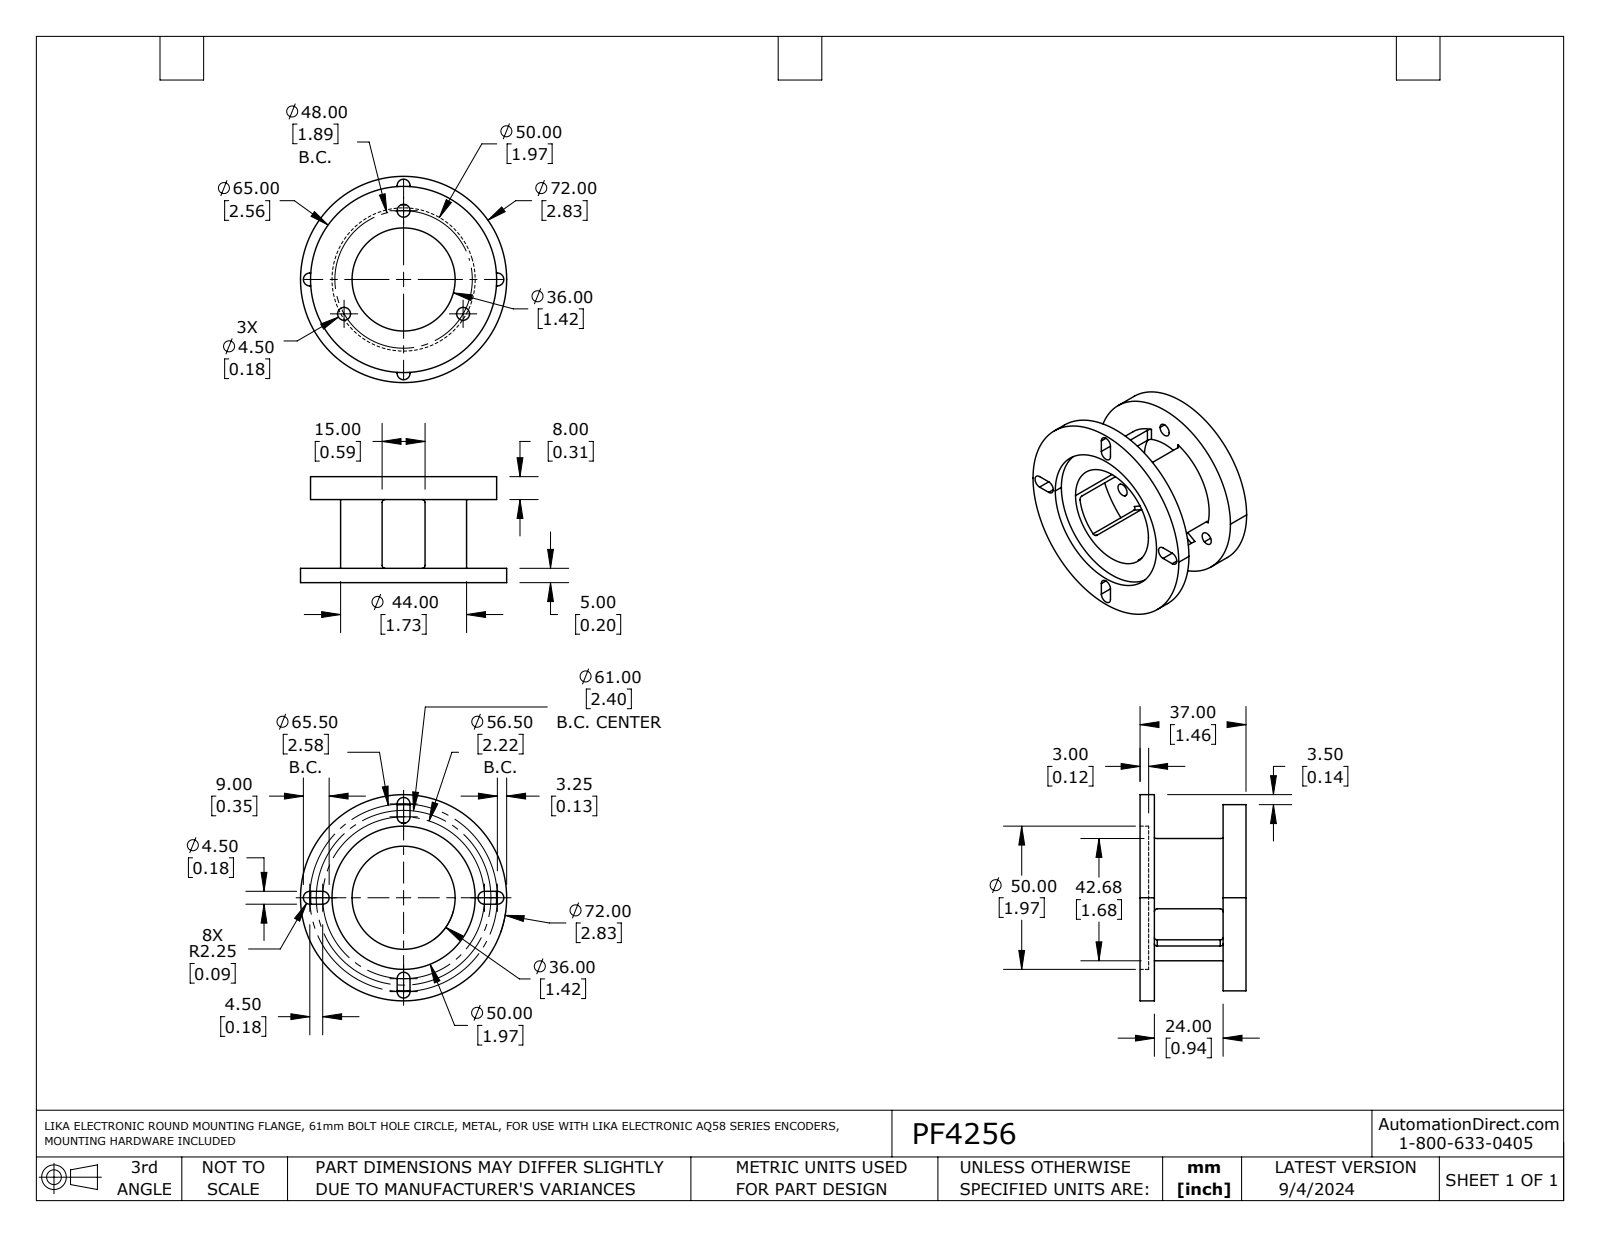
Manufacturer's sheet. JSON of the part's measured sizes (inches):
{"part_name": "PF4256", "step_written_by": "SolidWorks 2021 (AUTOMOTIVE_DESIGN)", "units": "inches", "bodies": {"solids": 1, "faces": 65, "planar": 19, "cylindrical": 46, "other": 0}, "overall_size": [2.835, 2.835, 1.457], "volume_in3": 2.281, "surface_area_in2": 29.88, "round_holes": [[0.177, 3], [1.417, 1], [1.969, 1]], "round_bosses_or_shafts": [[2.835, 1], [2.559, 1]], "partial_cylinders_radius": [[0.039, 12], [0.089, 8], [0.866, 1]], "face_to_face_distances": [1.26, 1.457, 0.197, 0.315, 0.945, 1.142, 1.339, 1.024, 0.079, 0.118], "hole_center_spacings": [0.945, 1.637, 1.636]}
